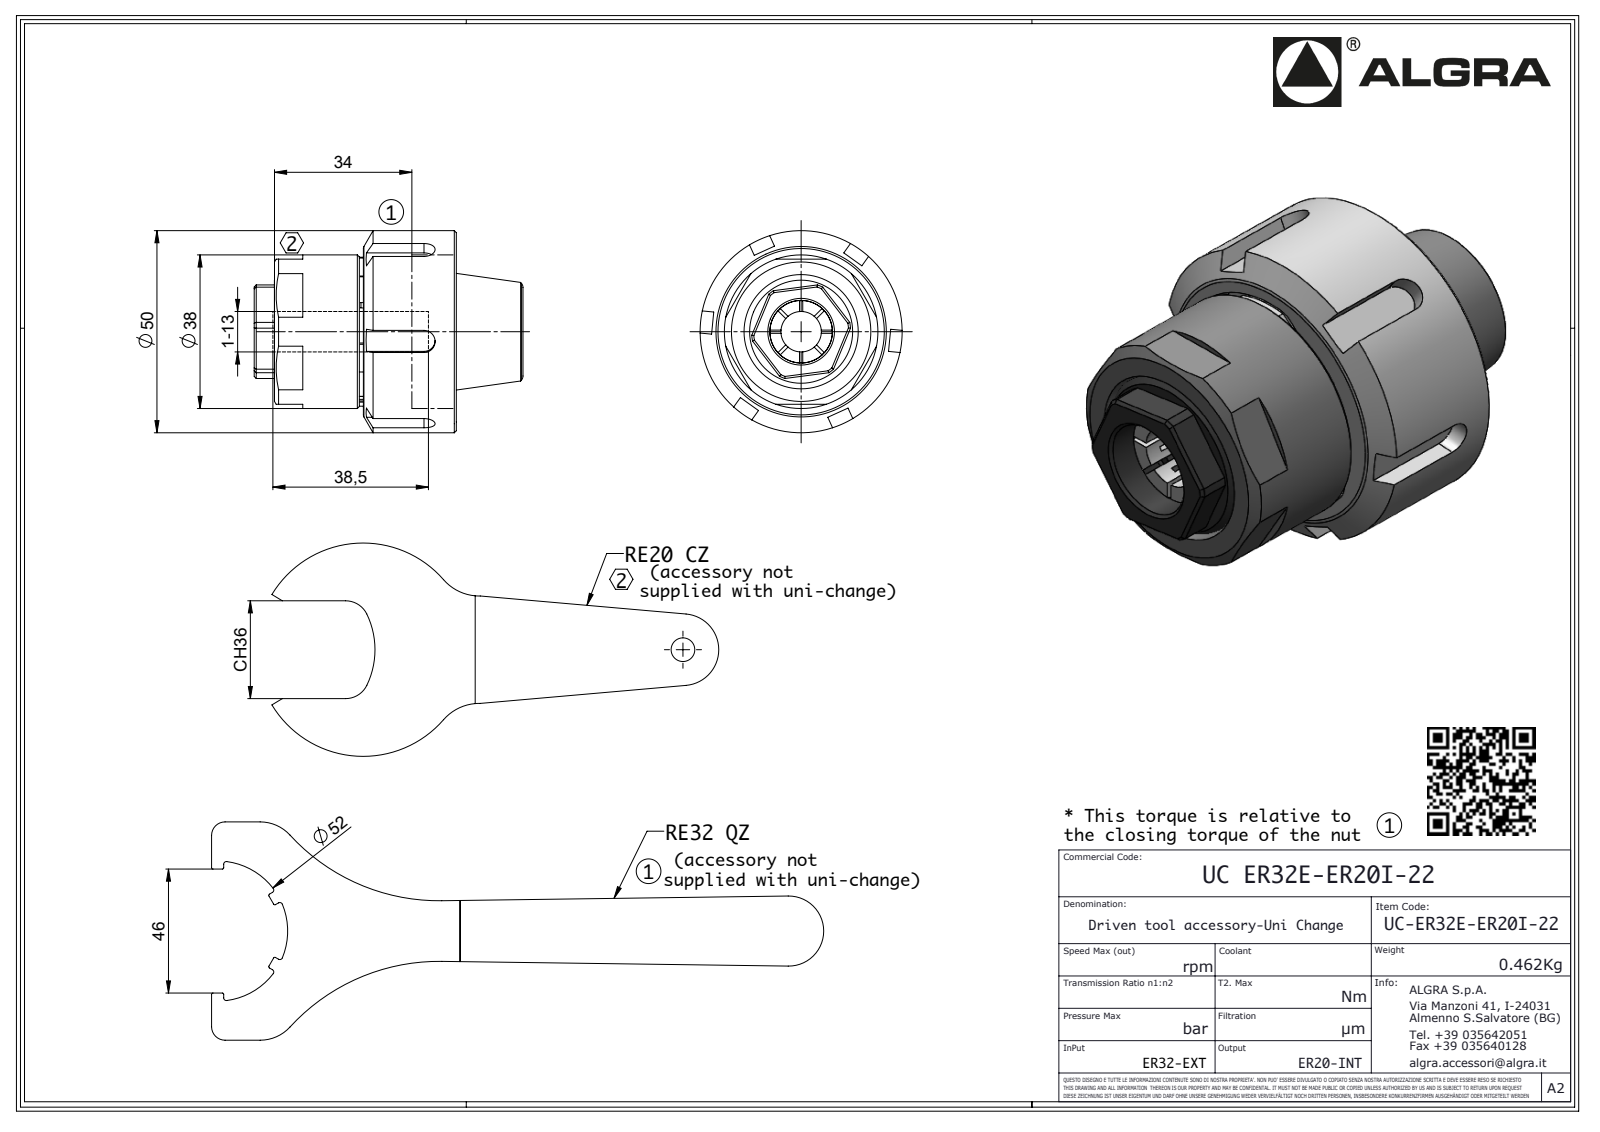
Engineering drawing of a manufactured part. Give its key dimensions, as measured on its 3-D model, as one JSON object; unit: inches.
{"part_name": "UCER32E-ER20I-22", "step_written_by": "SolidWorks 2016 (AUTOMOTIVE_DESIGN)", "units": "inches", "bodies": {"solids": 1, "faces": 427, "planar": 268, "cylindrical": 64, "other": 95}, "overall_size": [2.619, 1.969, 1.969], "volume_in3": 4.781, "surface_area_in2": 19.06, "round_holes": [[0.083, 1]], "round_bosses_or_shafts": [[1.969, 1], [1.496, 1], [0.251, 1], [0.067, 1]], "partial_cylinders_radius": [[0.008, 8], [0.013, 7], [0.02, 7], [0.146, 7], [0.108, 6], [0.079, 4], [0.059, 2], [0.008, 1]], "face_to_face_distances": [0.906, 0.866, 1.772, 0.65, 0.198, 1.064, 1.969, 2.619, 2.421, 1.555]}
